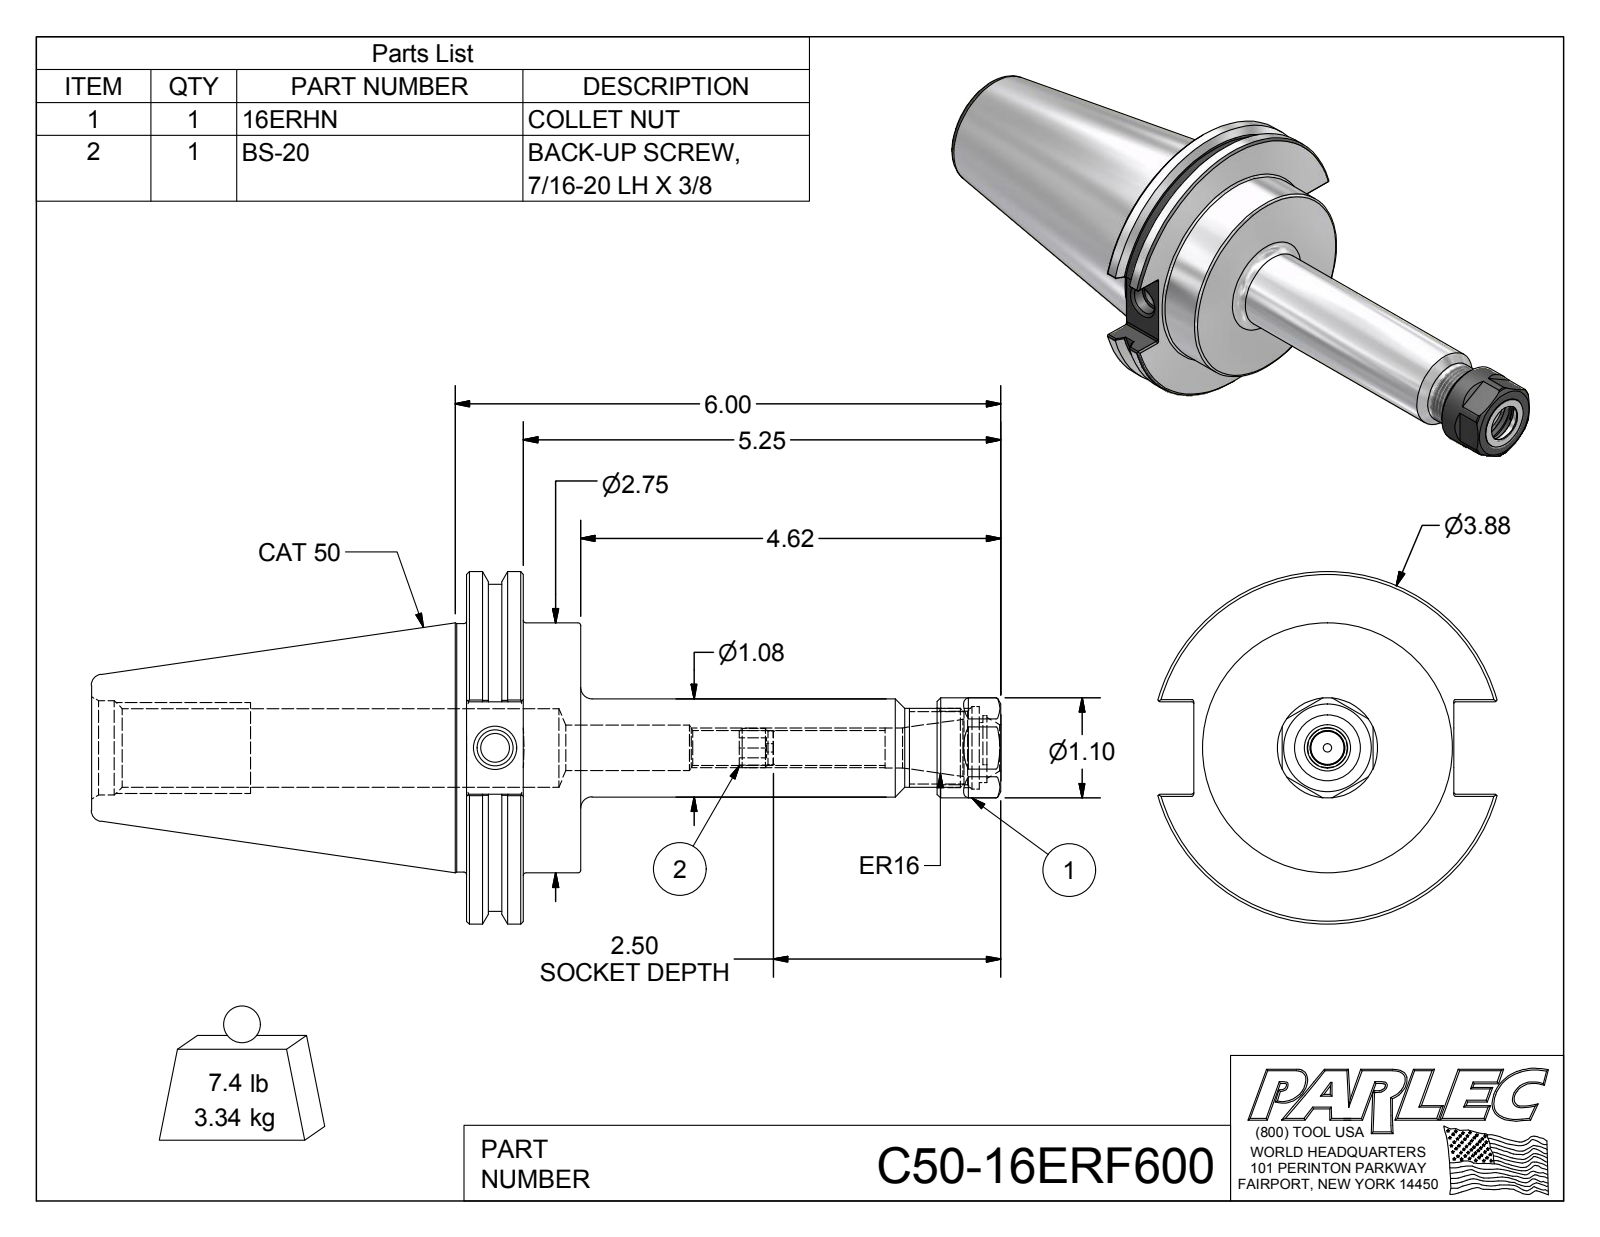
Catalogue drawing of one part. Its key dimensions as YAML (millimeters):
part_name: "C50-16ER6-1; 16ERHN; BS-20; C50-16ERF600"
step_written_by: "Autodesk Inventor 2016 (AUTOMOTIVE_DESIGN)"
units: millimeters
bodies: {solids: 3, faces: 145, planar: 59, cylindrical: 39, other: 47}
overall_size: [254, 98.42, 94.71]
volume: 428129
surface_area: 65237
round_holes:
  - {diameter: 2.29, count: 1}
  - {diameter: 8, count: 1}
  - {diameter: 9.73, count: 1}
  - {diameter: 10.13, count: 1}
  - {diameter: 11.18, count: 1}
  - {diameter: 12.4, count: 1}
  - {diameter: 12.7, count: 1}
  - {diameter: 17.02, count: 1}
  - {diameter: 20.5, count: 1}
  - {diameter: 21.97, count: 1}
  - {diameter: 23, count: 1}
  - {diameter: 26.37, count: 1}
round_bosses_or_shafts:
  - {diameter: 98.42, count: 1}
  - {diameter: 91.29, count: 1}
  - {diameter: 69.85, count: 1}
  - {diameter: 69.34, count: 1}
  - {diameter: 28, count: 1}
  - {diameter: 27.43, count: 1}
  - {diameter: 22, count: 1}
  - {diameter: 10.97, count: 1}
partial_cylinders:
  - {radius: 0.51, count: 12}
  - {radius: 7.24, count: 1}
  - {radius: 9, count: 1}
face_to_face_distances: [31.88, 15.88, 16, 149.23, 133.35, 117.35, 25.14, 104.77, 120.65, 136.65]
hole_center_spacings: [1.52]
